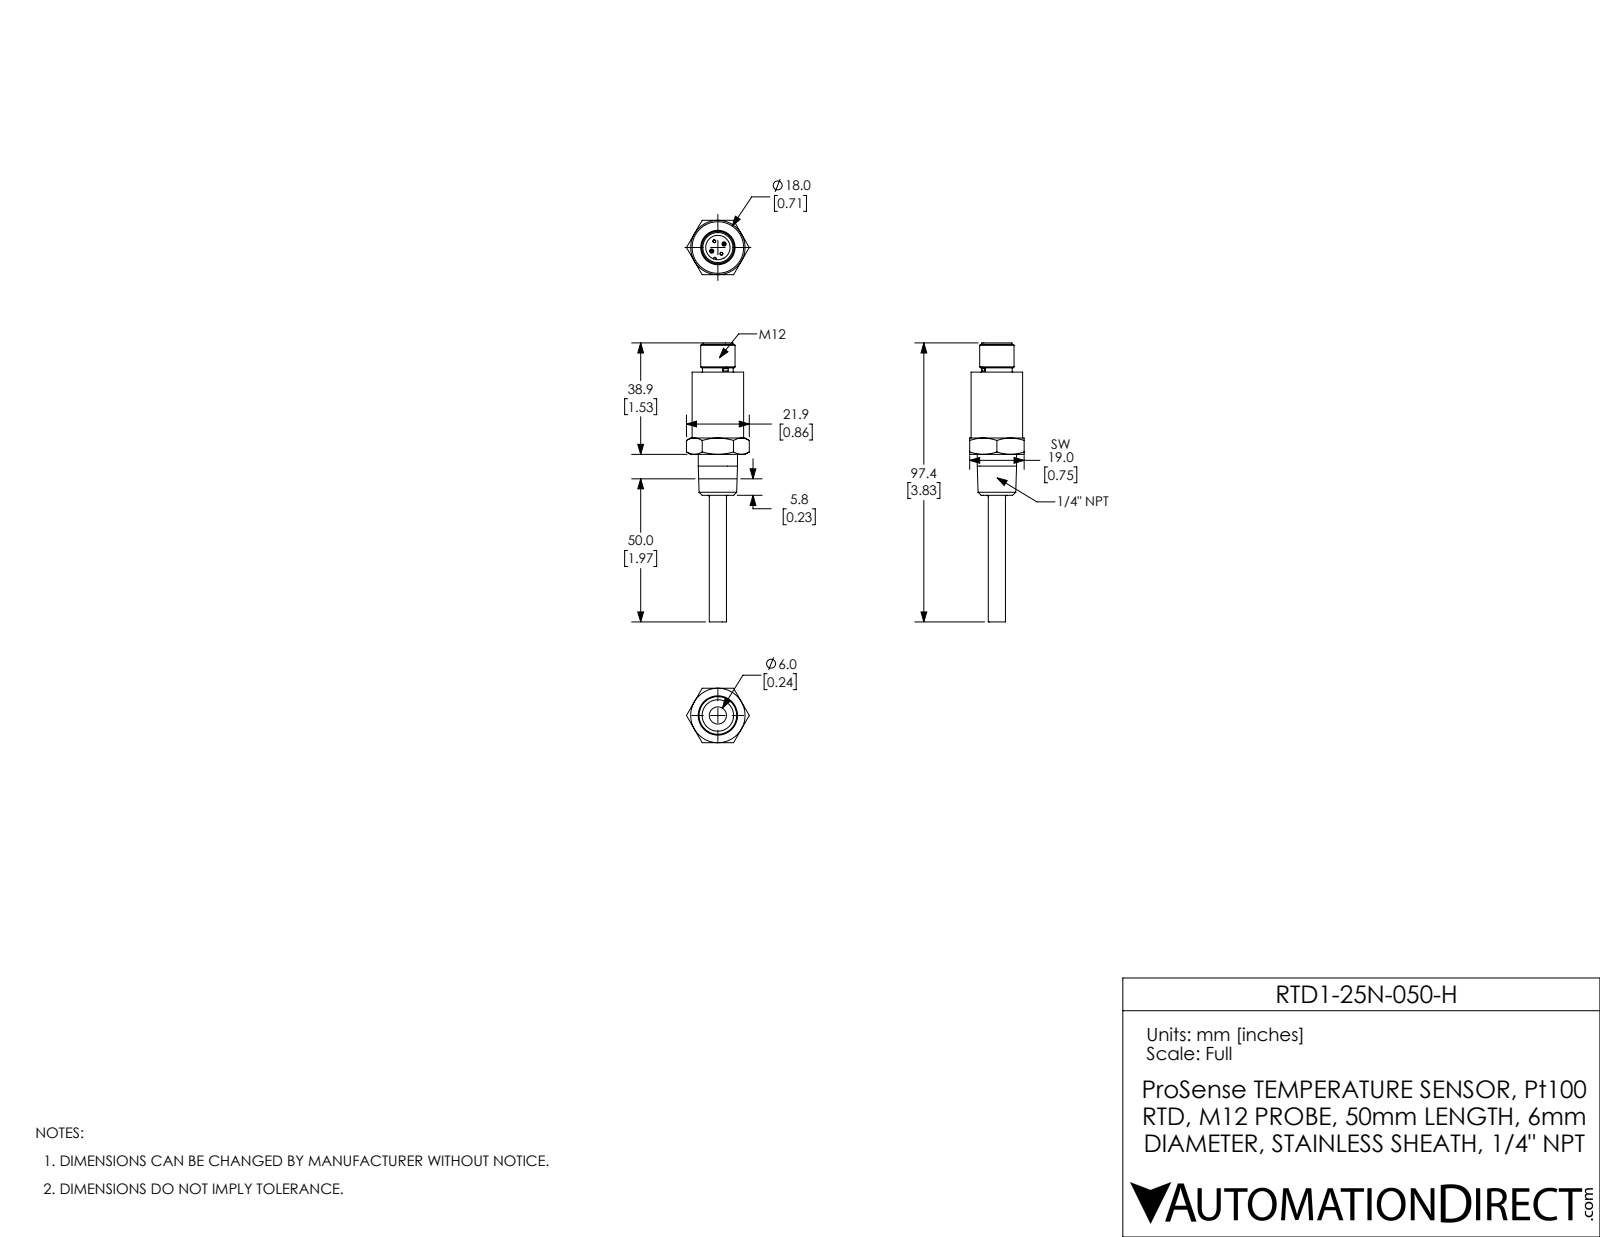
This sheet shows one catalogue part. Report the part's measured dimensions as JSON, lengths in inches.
{"part_name": "RTD1-25N-050-H", "step_written_by": "SolidWorks 2017 (AUTOMOTIVE_DESIGN)", "units": "inches", "bodies": {"solids": 1, "faces": 95, "planar": 32, "cylindrical": 23, "other": 40}, "overall_size": [3.835, 0.864, 0.748], "volume_in3": 0.702, "surface_area_in2": 6.773, "round_holes": [[0.335, 1]], "round_bosses_or_shafts": [[0.04, 4], [0.709, 1], [0.54, 1], [0.472, 1], [0.421, 1], [0.413, 1], [0.236, 1]], "partial_cylinders_radius": [[0.016, 1]], "face_to_face_distances": [0.748, 1.13, 1.74, 0.563, 1.693, 1.177, 0.047, 2.094, 1.531, 0.402]}
